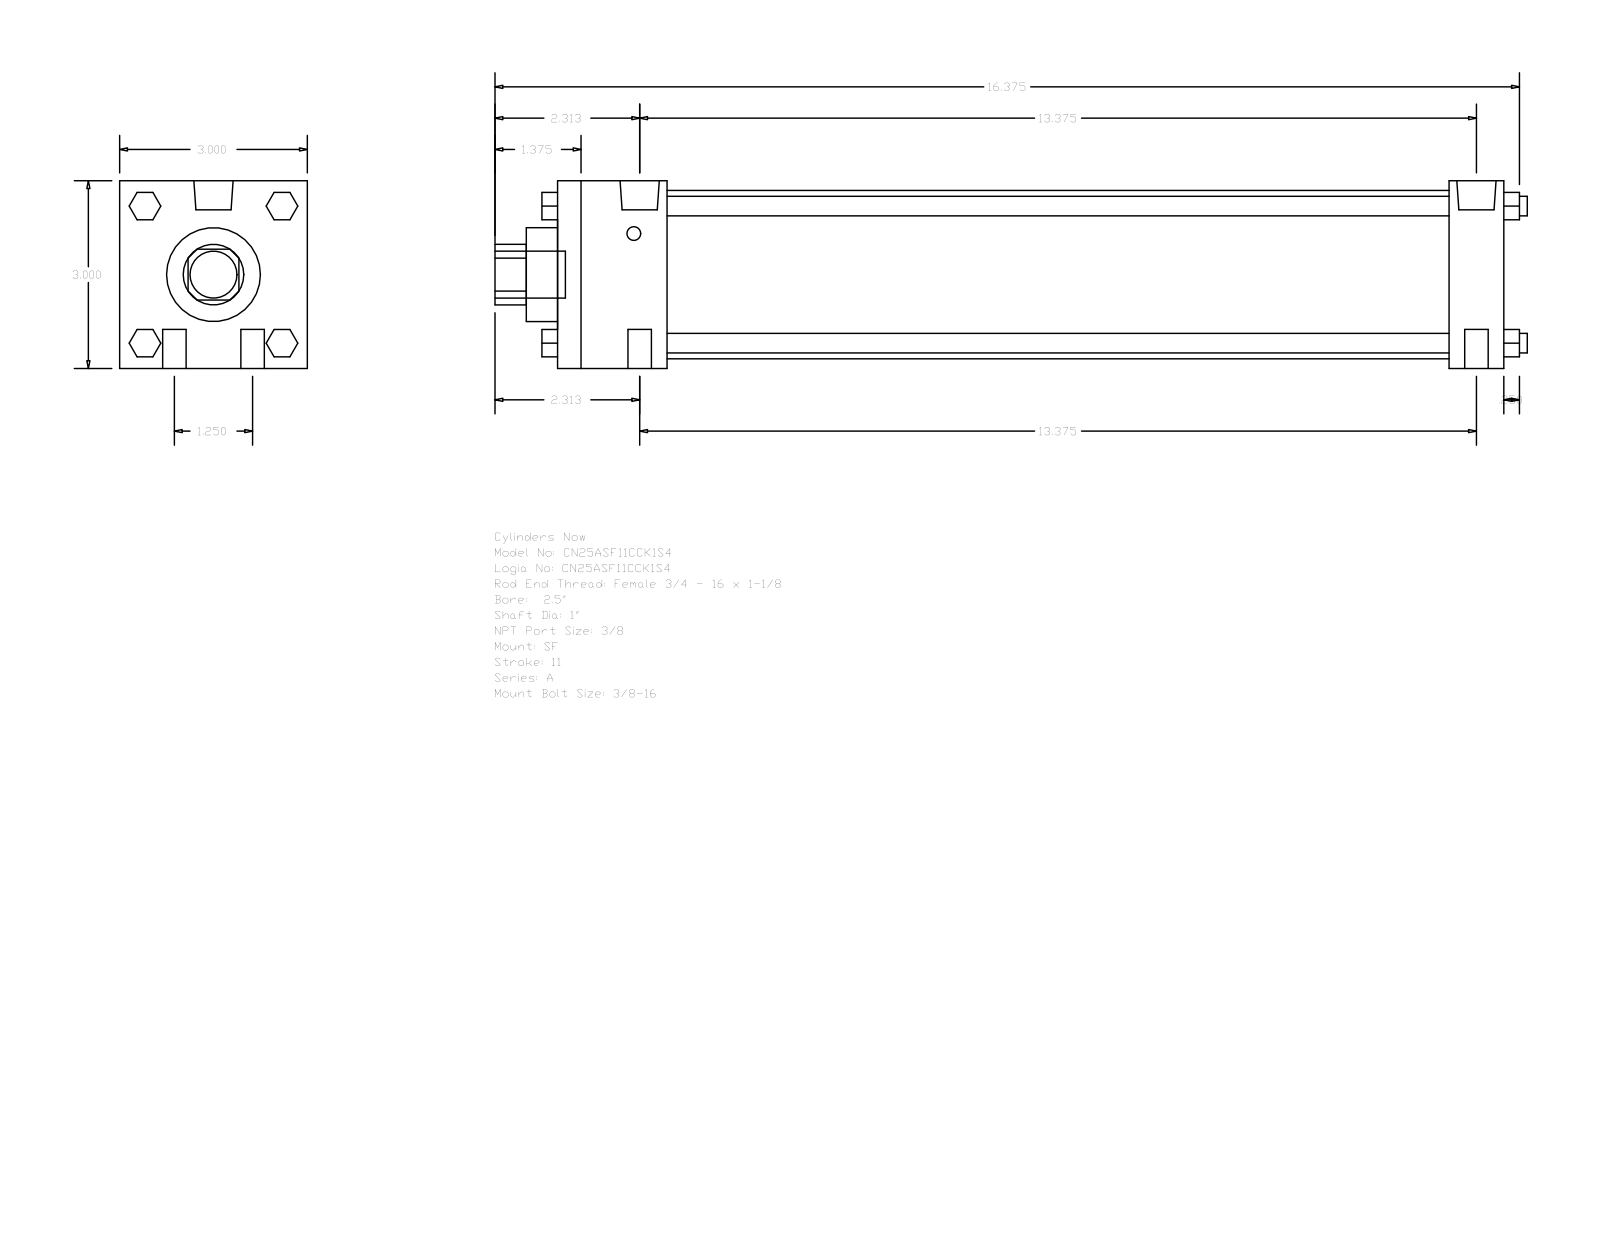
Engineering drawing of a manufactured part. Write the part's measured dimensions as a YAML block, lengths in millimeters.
part_name: "A_SF__0250_1"
step_written_by: "GSSL Pune (CONFIG_CONTROL_DESIGN)"
units: millimeters
bodies: {solids: 0, faces: 124, planar: 94, cylindrical: 30, other: 0}
overall_size: [419.1, 76.2, 76.2]
round_holes:
  - {diameter: 25.4, count: 1}
  - {diameter: 38.1, count: 1}
  - {diameter: 68.33, count: 1}
round_bosses_or_shafts:
  - {diameter: 9.53, count: 4}
  - {diameter: 7.94, count: 4}
  - {diameter: 15.93, count: 2}
  - {diameter: 5.56, count: 2}
  - {diameter: 19.05, count: 1}
partial_cylinders:
  - {radius: 12.29, count: 1}
face_to_face_distances: [76.2, 384.17, 361.95, 22.22, 44.45, 317.5, 339.72, 12.7, 11.11, 57.15]
